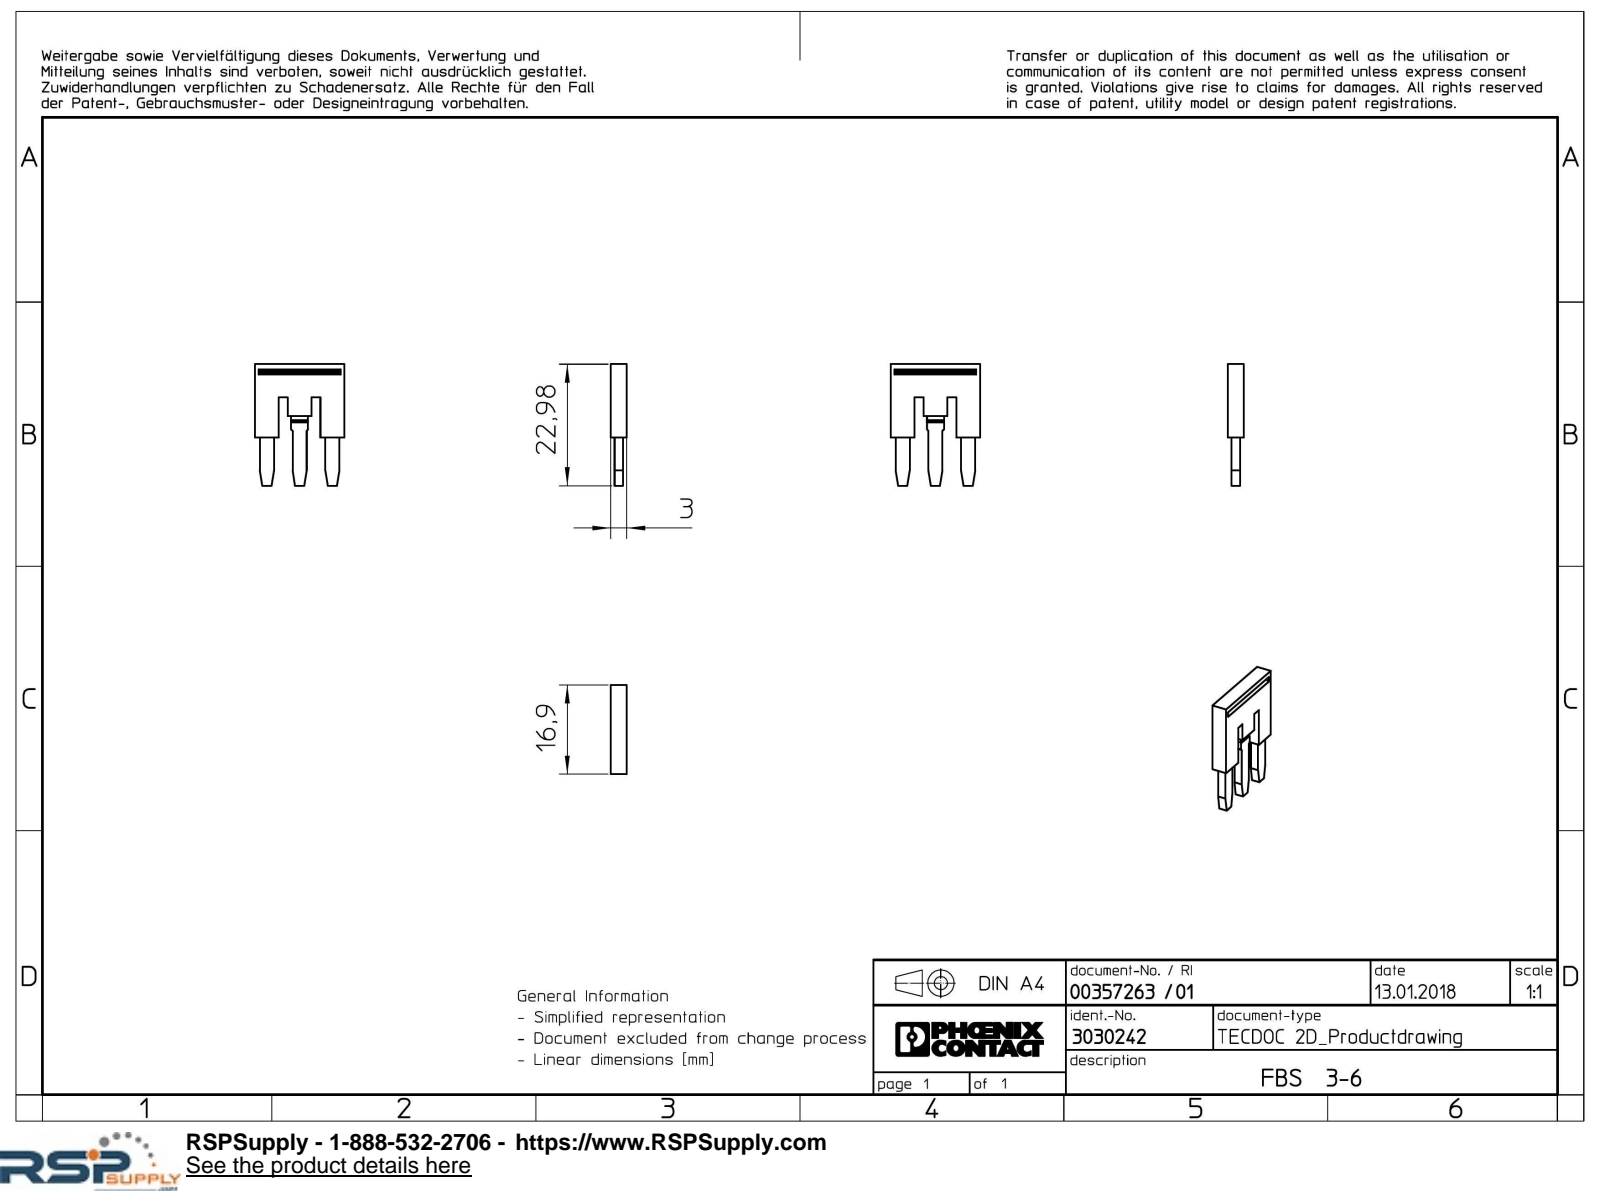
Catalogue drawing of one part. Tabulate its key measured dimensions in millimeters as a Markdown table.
| quantity | value |
| --- | --- |
| part name | FBS_3-6_select |
| STEP written by | Creo Elements/Direct Modeling 20.1A 29-Sep-2018 (C) Parametric Technology GmbH (AUTOMOTIVE_DESIGN) |
| units | millimeters |
| bodies | 1 solid, 55 faces (55 planar, 0 cylindrical, 0 other) |
| overall size | 22.98 × 16.9 × 3 |
| volume | 681 mm³ |
| surface area | 941 mm² |
| main face-to-face distances | 3, 0.7, 2.3, 6.2, 1.6, 12.4, 0.91, 3.59, 4.5, 9.79 |
